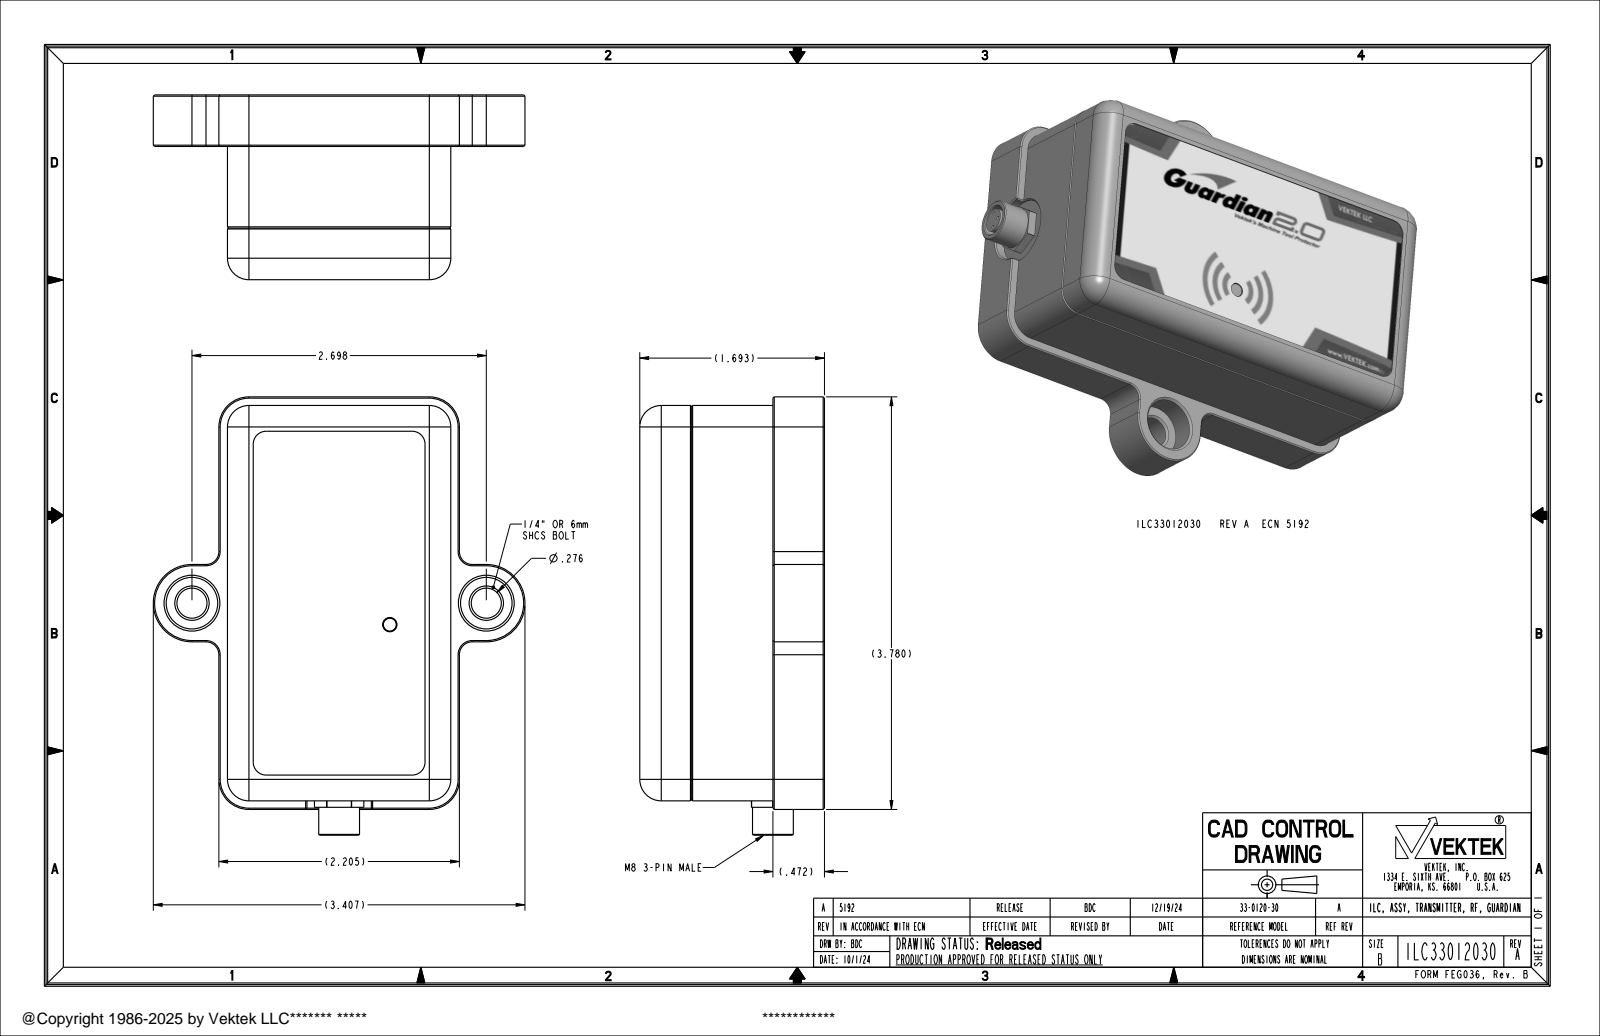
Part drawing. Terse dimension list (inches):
name: ILC33012030
written by: CREO PARAMETRIC BY PTC INC, 2021164 (AUTOMOTIVE_DESIGN)
unit: in
bodies: 1 solid, 382 faces (156 planar, 90 cylindrical, 136 other)
size: 4.016 × 3.407 × 1.693
volume: 13.01 in³; area: 41.26 in²
holes: 4× ⌀0.138, 3× ⌀0.031, 3× ⌀0.276, 2× ⌀0.472, 1× ⌀0.13, 1× ⌀0.591
bosses: 4× ⌀0.22, 4× ⌀0.118, 1× ⌀0.374, 1× ⌀0.217, 1× ⌀0.126
rounds: 8× R0.118, 8× R0.197, 4× R0.211, 4× R0.217, 4× R0.276, 2× R0.354, 1× R0.226
face distances: 1.681, 0.079, 2.047, 2.126, 3.622, 3.701, 0.472, 0.02, 1.209, 2.205
hole spacings: 1.696, 2.709, 0.069, 0.097, 1.654, 3.228, 3.627, 0.138
